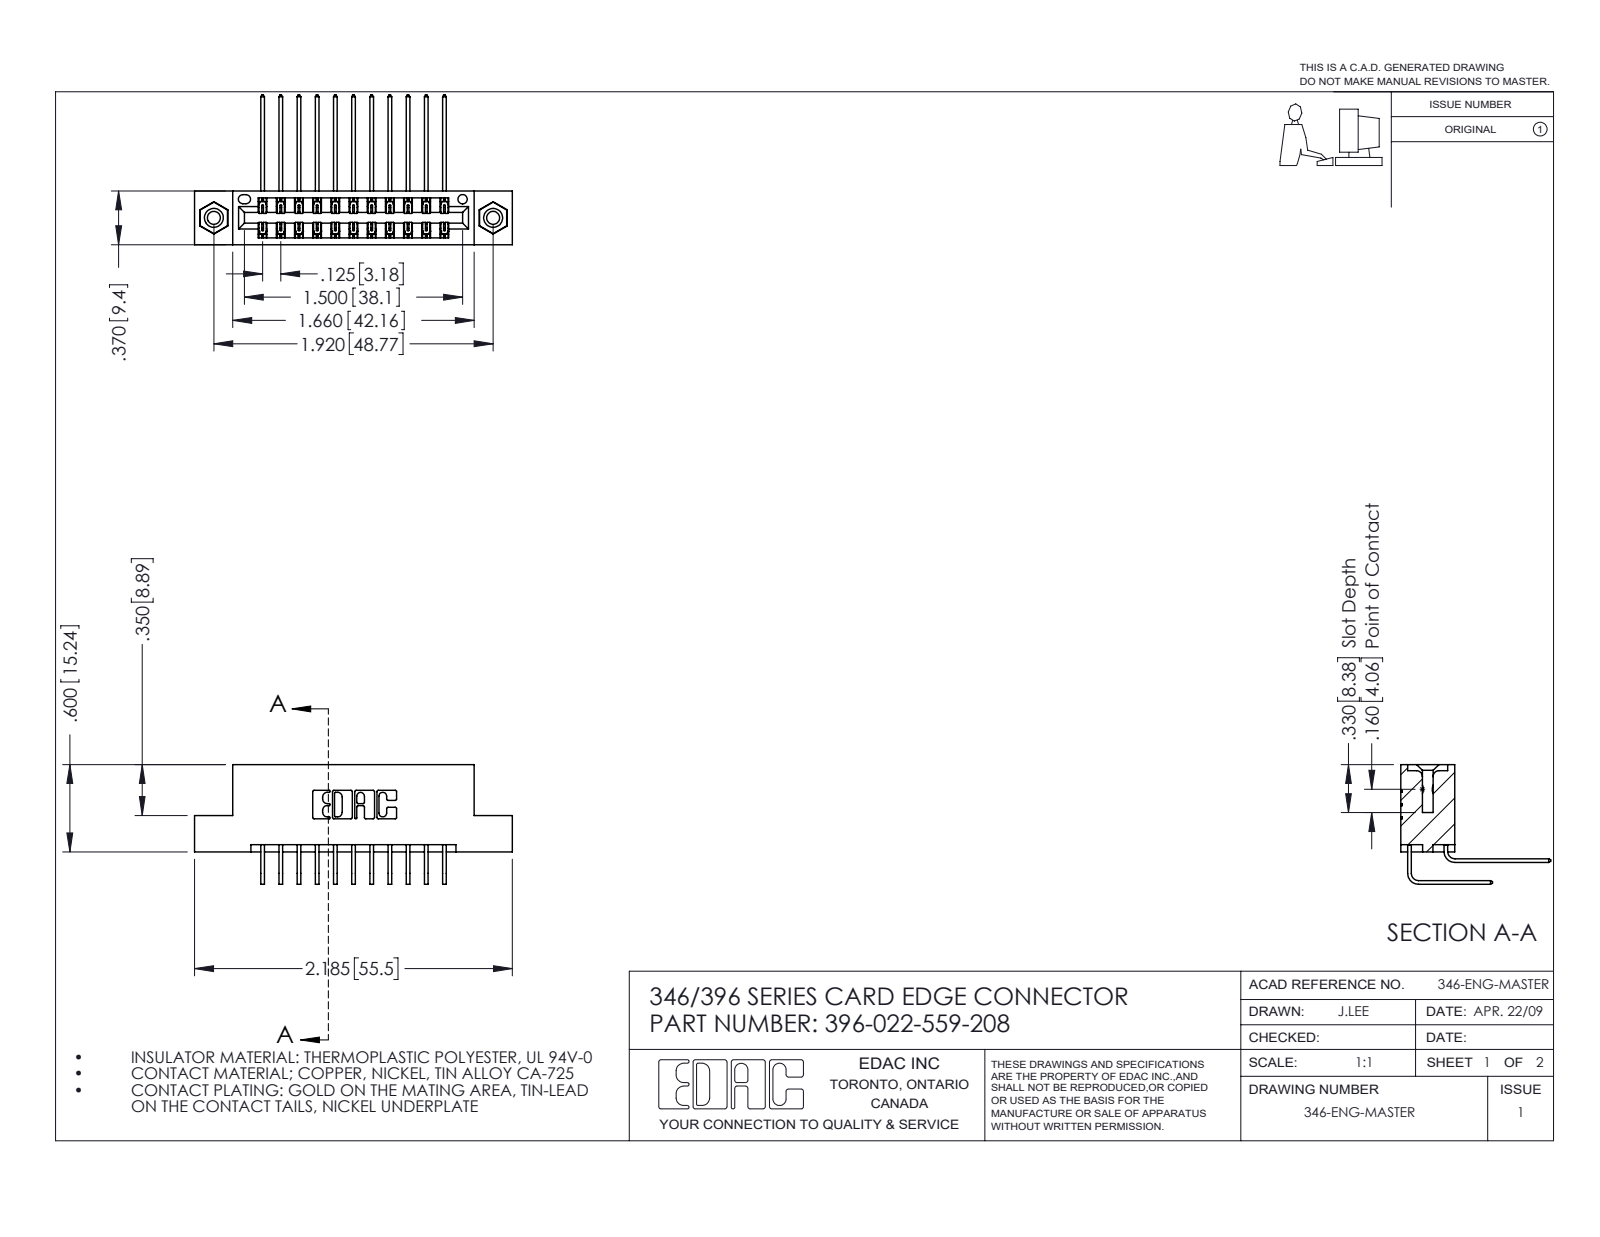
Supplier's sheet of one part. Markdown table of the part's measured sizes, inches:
| quantity | value |
| --- | --- |
| part name | 345-292-001_559 Tail - 2; 345-292-001_558 559 Tail - 1; 396-022-559-208; 346 Part_Flush Mounting Lugs - 0.156 Dia-TI (+1 more) |
| STEP written by | SolidWorks 2016 (CONFIG_CONTROL_DESIGN) |
| units | inches |
| bodies | 25 solids, 1370 faces (922 planar, 432 cylindrical, 16 other) |
| overall size | 2.185 × 1.03 × 0.823 |
| volume | 0.323 in³ |
| surface area | 11.49 in² |
| round holes (diameter × count) | 0.089 × 2, 0.125 × 2, 0.156 × 2, 0.064 × 1 |
| round bosses / shafts (diameter × count) | 0.155 × 2 |
| partial cylindrical surfaces (radius × count) | 0.006 × 33, 0.01 × 22, 0.007 × 6, 0.031 × 6, 0.026 × 3, 0.014 × 2, 0.022 × 2, 0.024 × 2 |
| main face-to-face distances | 0.25, 0.048, 0.322, 0.37, 0.025, 0.072, 0.298, 0.275, 0.148, 0.222 |
| hole center spacings | 0.246, 1.715, 1.92 |
